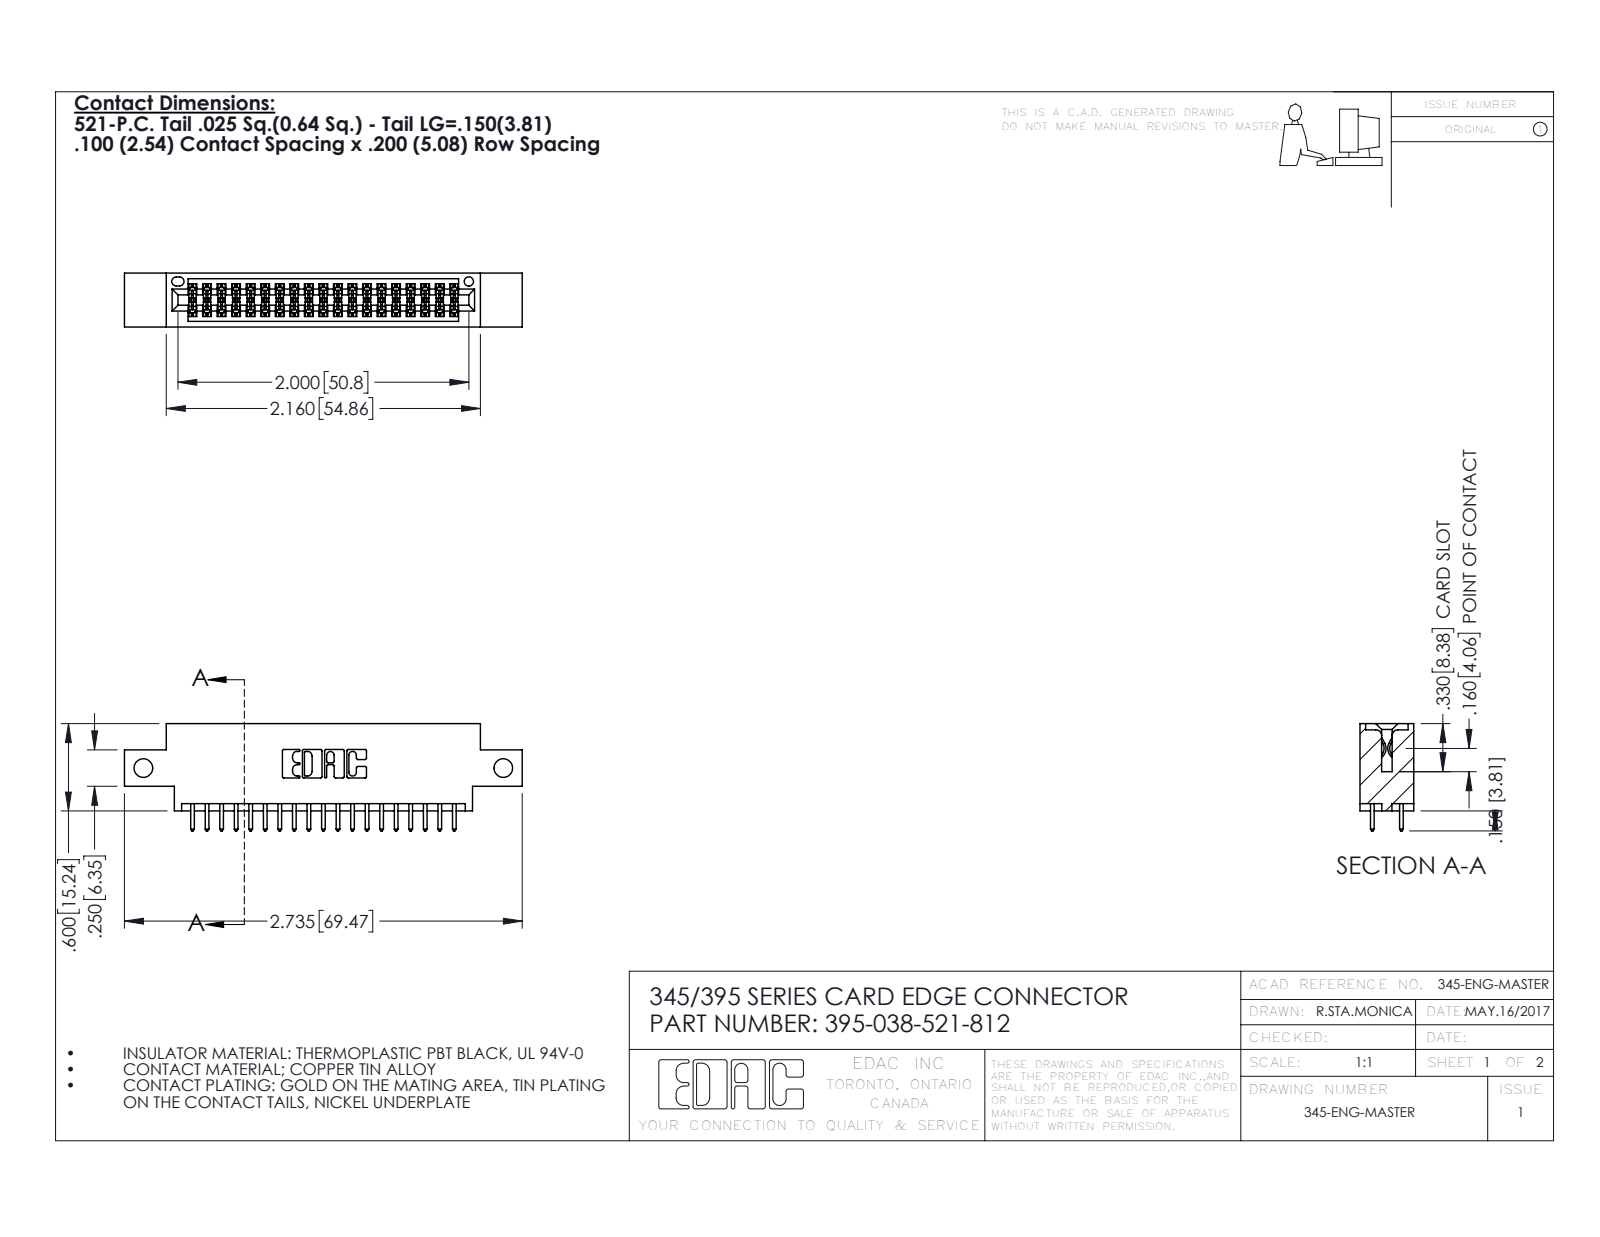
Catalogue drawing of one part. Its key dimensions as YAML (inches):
part_name: "395-038-521-812; 345-292-001_345-293-121; 345 Part_0.170 Offset - Side Mount"
step_written_by: "SolidWorks 2016 (CONFIG_CONTROL_DESIGN)"
units: inches
bodies: {solids: 39, faces: 2030, planar: 1338, cylindrical: 692, other: 0}
overall_size: [2.735, 0.737, 0.37]
volume: 0.386
surface_area: 13.64
round_holes:
  - {diameter: 0.128, count: 2}
  - {diameter: 0.064, count: 1}
partial_cylinders:
  - {radius: 0.006, count: 57}
  - {radius: 0.01, count: 38}
  - {radius: 0.01, count: 22}
  - {radius: 0.007, count: 6}
  - {radius: 0.031, count: 6}
  - {radius: 0.026, count: 3}
  - {radius: 0.014, count: 2}
  - {radius: 0.019, count: 2}
face_to_face_distances: [0.298, 0.072, 0.37, 0.2, 0.098, 0.272, 0.025, 0.225, 0.175, 0.1]
hole_center_spacings: [2.475]
